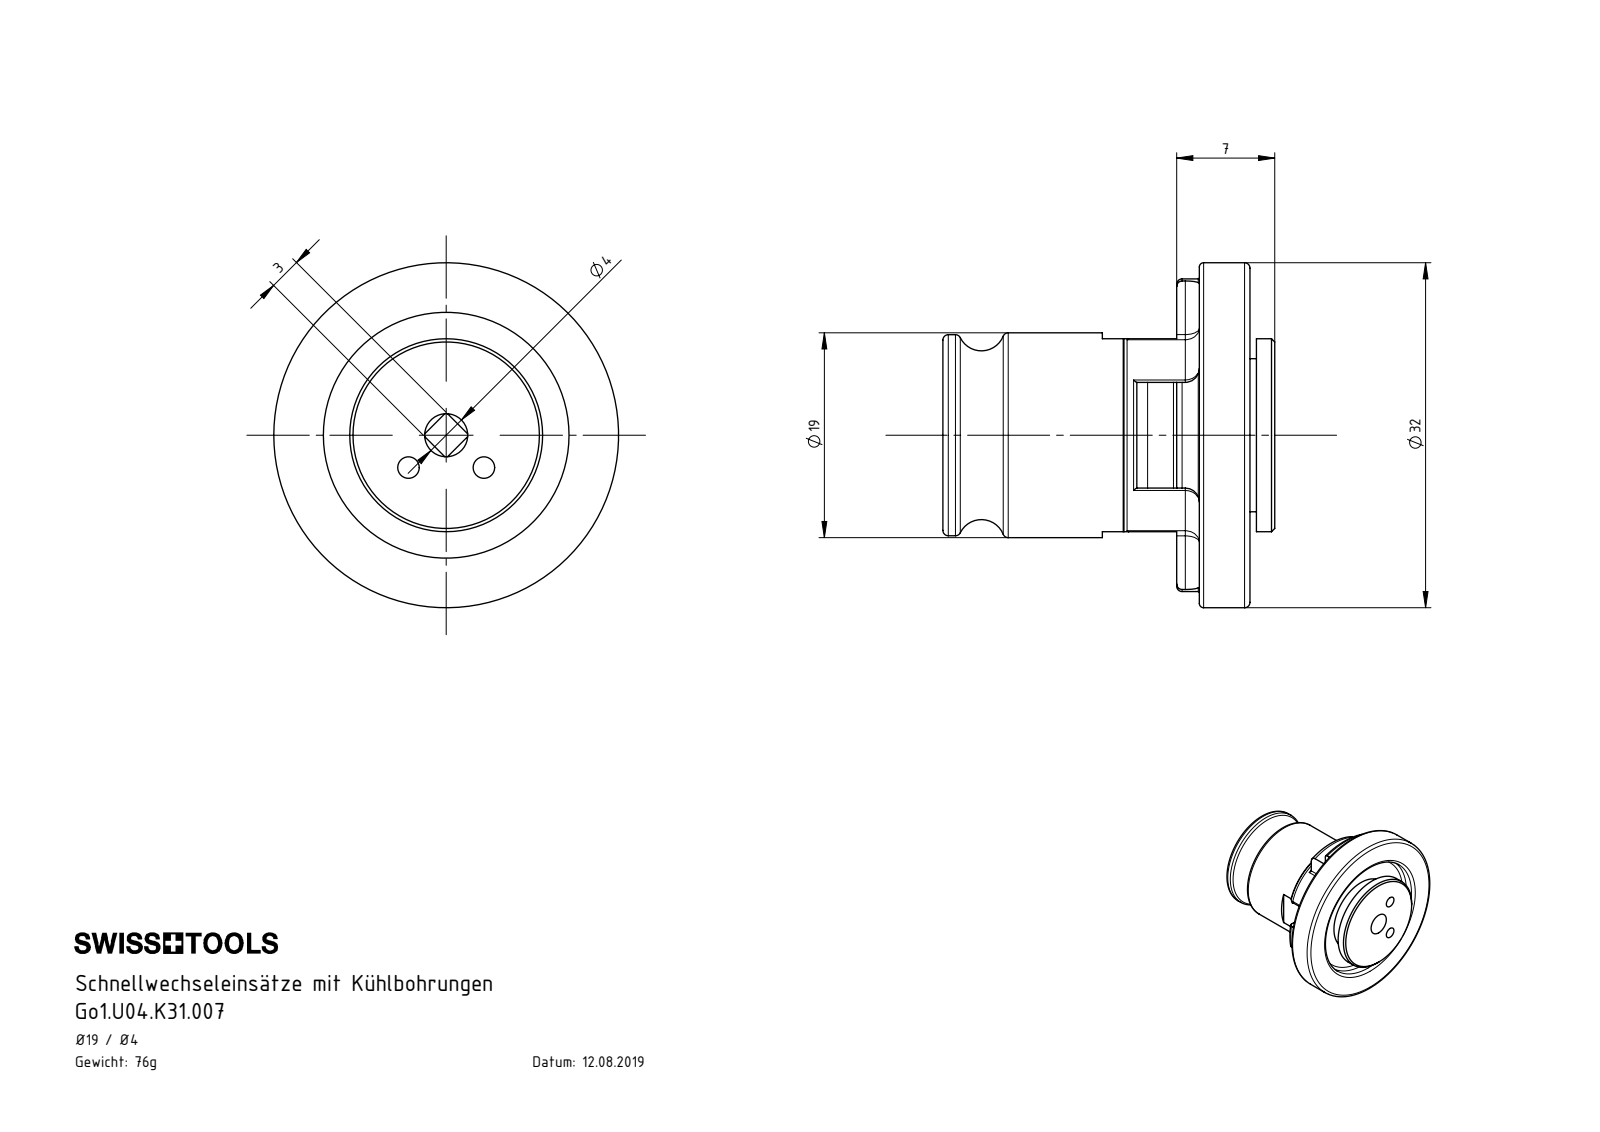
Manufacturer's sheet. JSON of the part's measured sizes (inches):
{"part_name": "Go1.U04.K31.007", "step_written_by": "SolidWorks 2017 (AUTOMOTIVE_DESIGN)", "units": "inches", "bodies": {"solids": 1, "faces": 114, "planar": 36, "cylindrical": 34, "other": 44}, "overall_size": [1.26, 1.26, 1.213], "volume_in3": 0.592, "surface_area_in2": 7.442, "round_holes": [[0.079, 2], [0.157, 1], [0.449, 1], [0.898, 1]], "round_bosses_or_shafts": [[1.26, 1], [0.748, 1], [0.734, 1], [0.729, 1], [0.705, 1], [0.559, 1]], "partial_cylinders_radius": [[0.02, 8], [0.051, 4], [0.488, 1], [0.571, 1]], "face_to_face_distances": [0.093, 0.185, 0.276, 0.091, 0.183, 0.937, 1.03, 1.122, 1.213, 1.146], "hole_center_spacings": [0.181, 0.276]}
